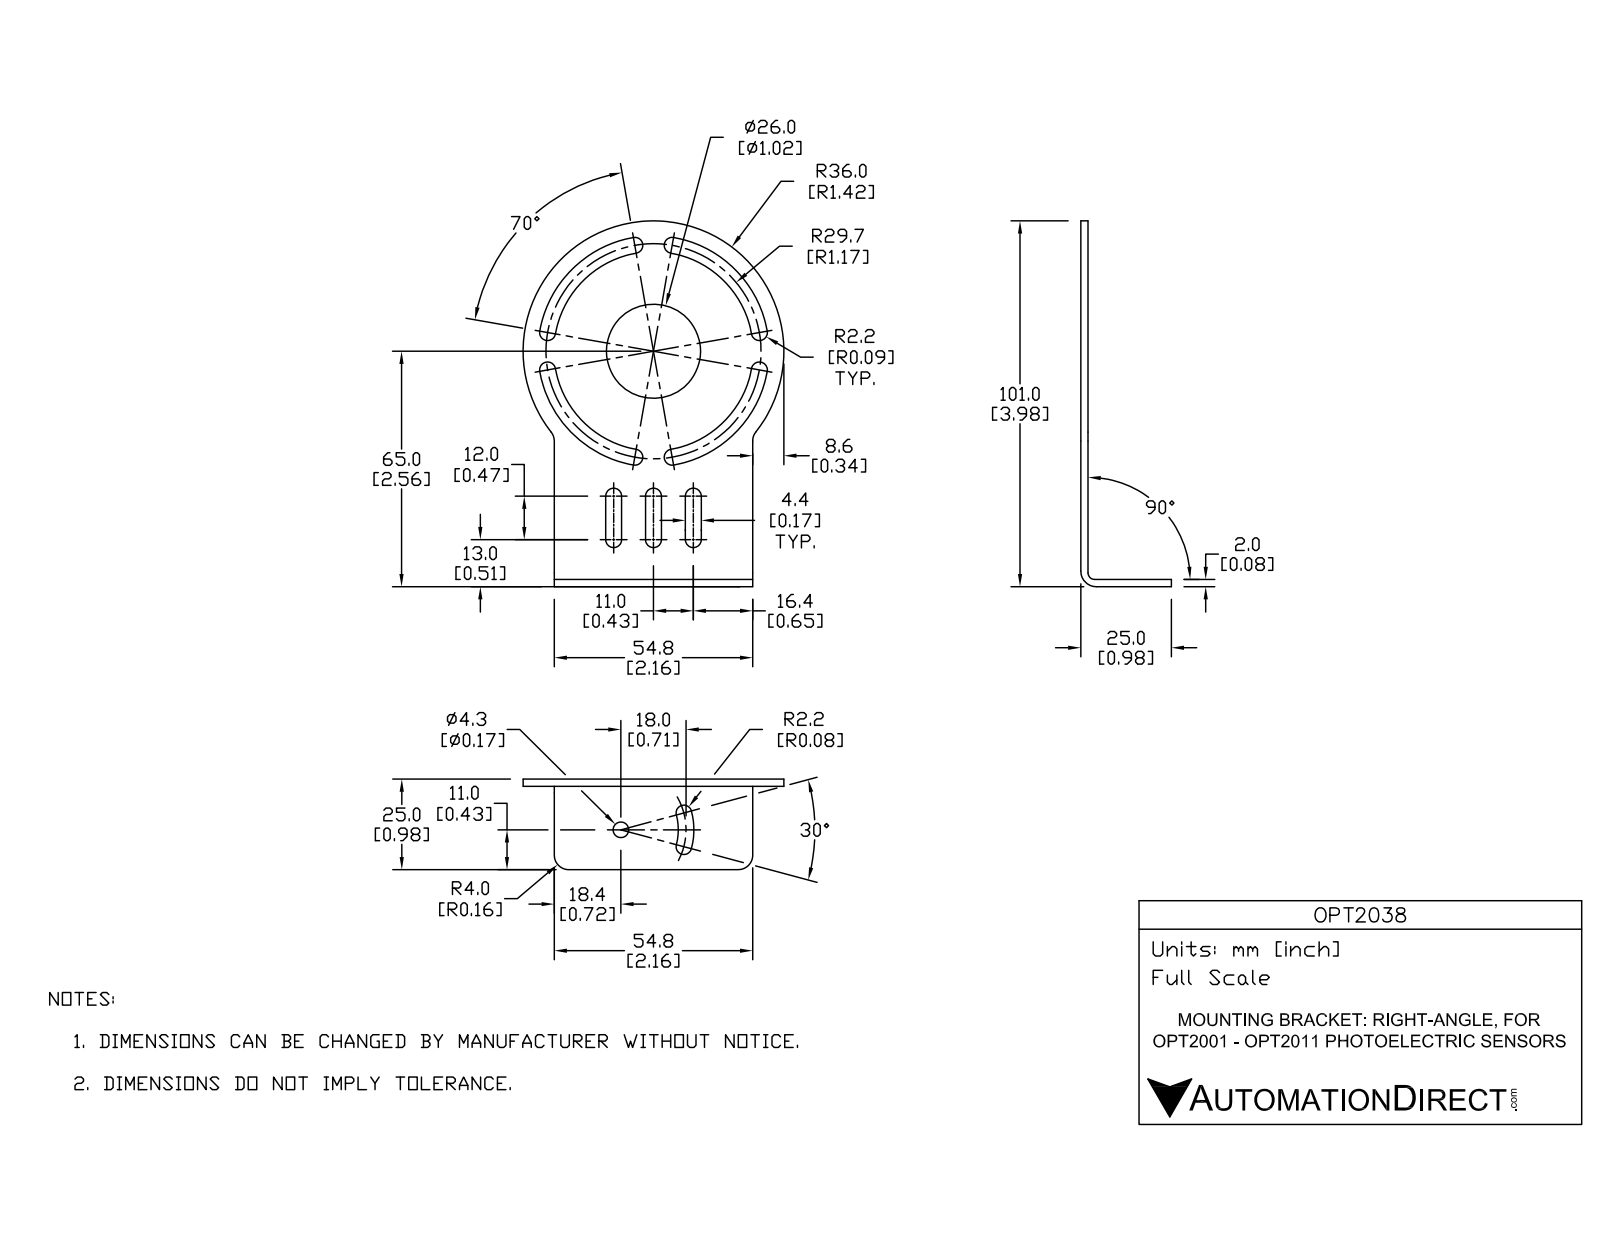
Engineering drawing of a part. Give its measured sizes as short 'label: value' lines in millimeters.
name: 1025676
written by: ST-DEVELOPER v16.7 (AUTOMOTIVE_DESIGN)
unit: mm
bodies: 1 solid, 48 faces (13 planar, 35 cylindrical, 0 other)
size: 101 × 72 × 25
volume: 11 066 mm³; area: 12 957 mm²
holes: 1× ⌀4.3, 1× ⌀26
rounds: 14× R2.2, 4× R4, 2× R2.15, 1× R1.8, 1× R4.3, 1× R15.85, 1× R20.15, 1× R27.5
face distances: 2, 54.8, 11, 23, 25, 4.4, 25.2, 29.6, 18.6, 36.2
